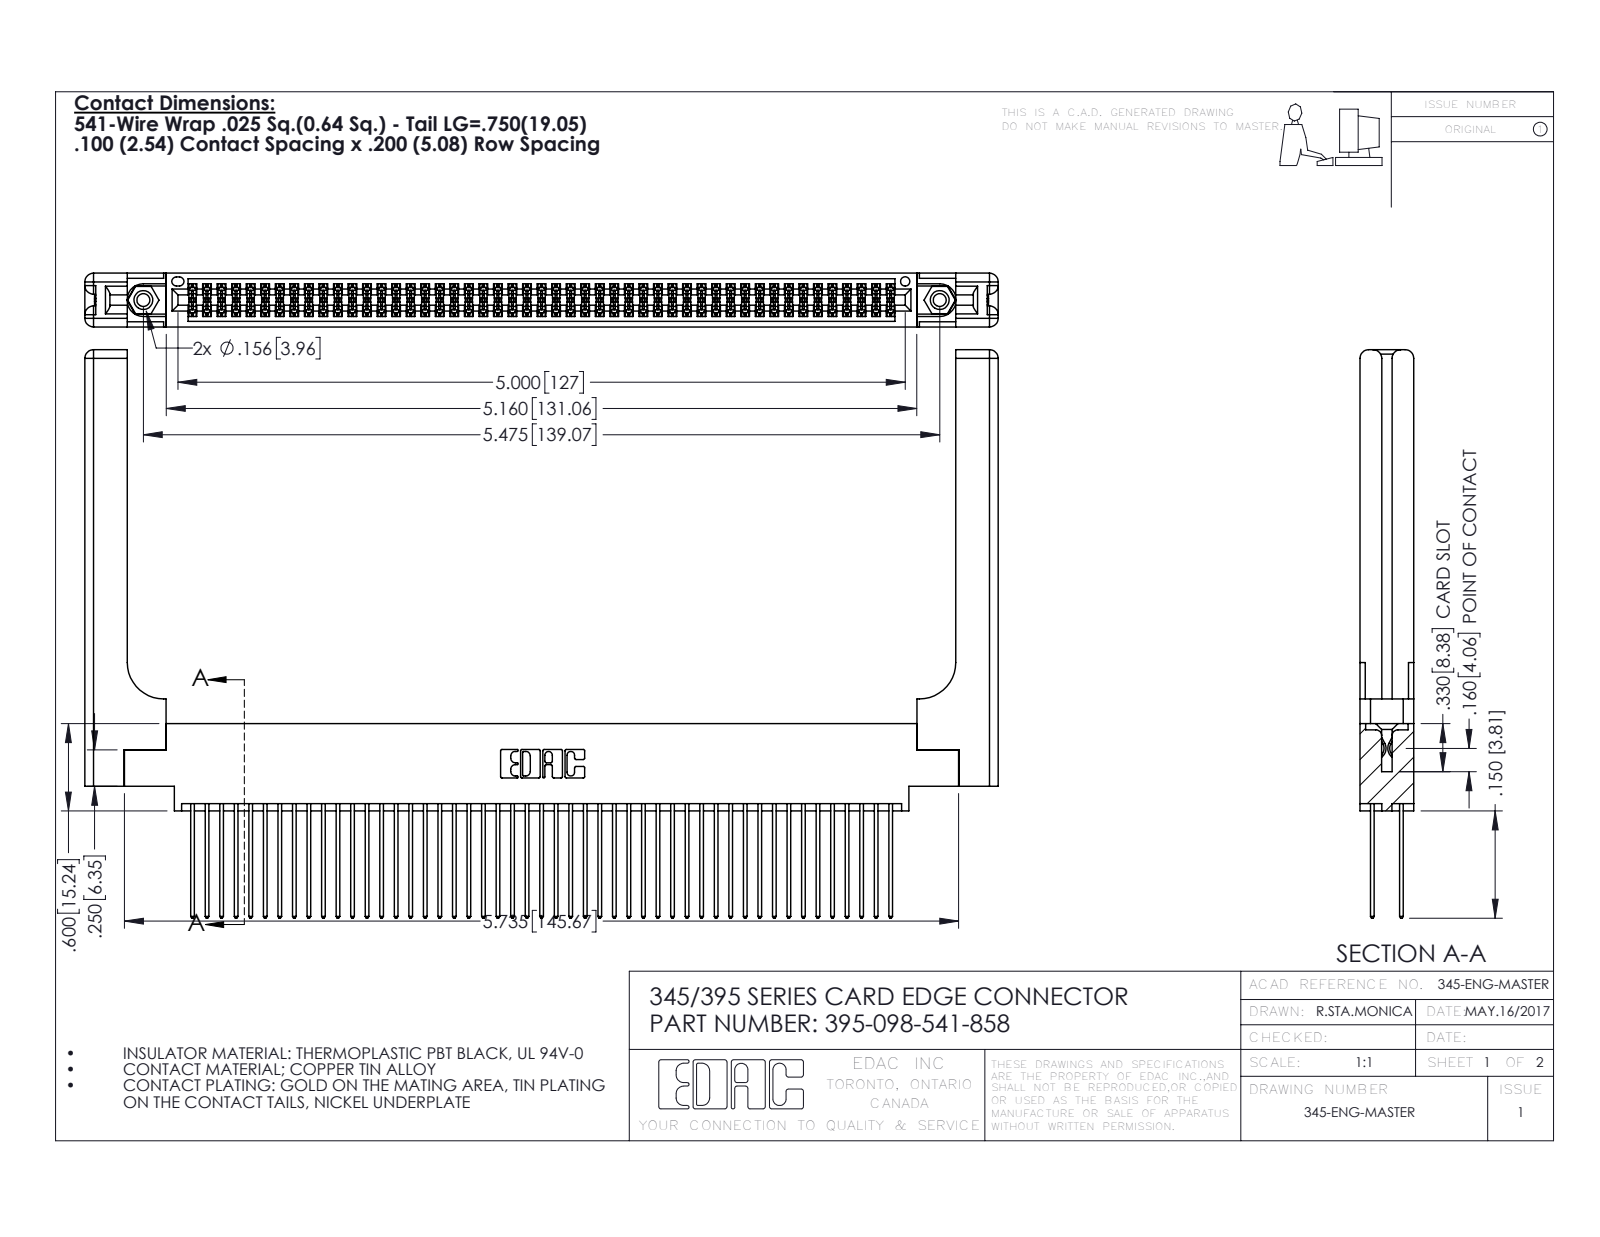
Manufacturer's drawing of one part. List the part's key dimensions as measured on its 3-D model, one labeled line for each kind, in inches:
Part name (STEP PRODUCT): 395-098-541-858; 345 Part_0.170 Offset - 0.156 Dia-TH; 345-250-001_345-250-001-102; 345-220-058_345-220-058 (+1 more)
STEP written by: SolidWorks 2016 (CONFIG_CONTROL_DESIGN)
Units: inches
Bodies: 103 solids, 5286 faces (3466 planar, 1760 cylindrical, 60 other)
Overall size (bounding box): 6.279 × 3.907 × 0.37
Volume: 1.494 in³ · Surface area: 49.04 in²
Round holes (diameter × count): ⌀0.089 ×2, ⌀0.125 ×2, ⌀0.156 ×2, ⌀0.064 ×1
Round bosses / shafts (diameter × count): ⌀0.155 ×2
Partial cylindrical surfaces — rounded edges, fillets, slot ends (radius × count): R0.006 ×147, R0.01 ×98, R0.01 ×22, R0.06 ×16, R0.007 ×6, R0.031 ×6, R0.026 ×3, R0.014 ×2
Main face-to-face distances: 0.072, 0.298, 0.37, 0.098, 0.272, 0.025, 0.2, 0.225, 0.175, 0.148
Hole centre spacings: 0.27, 5.239, 5.475
